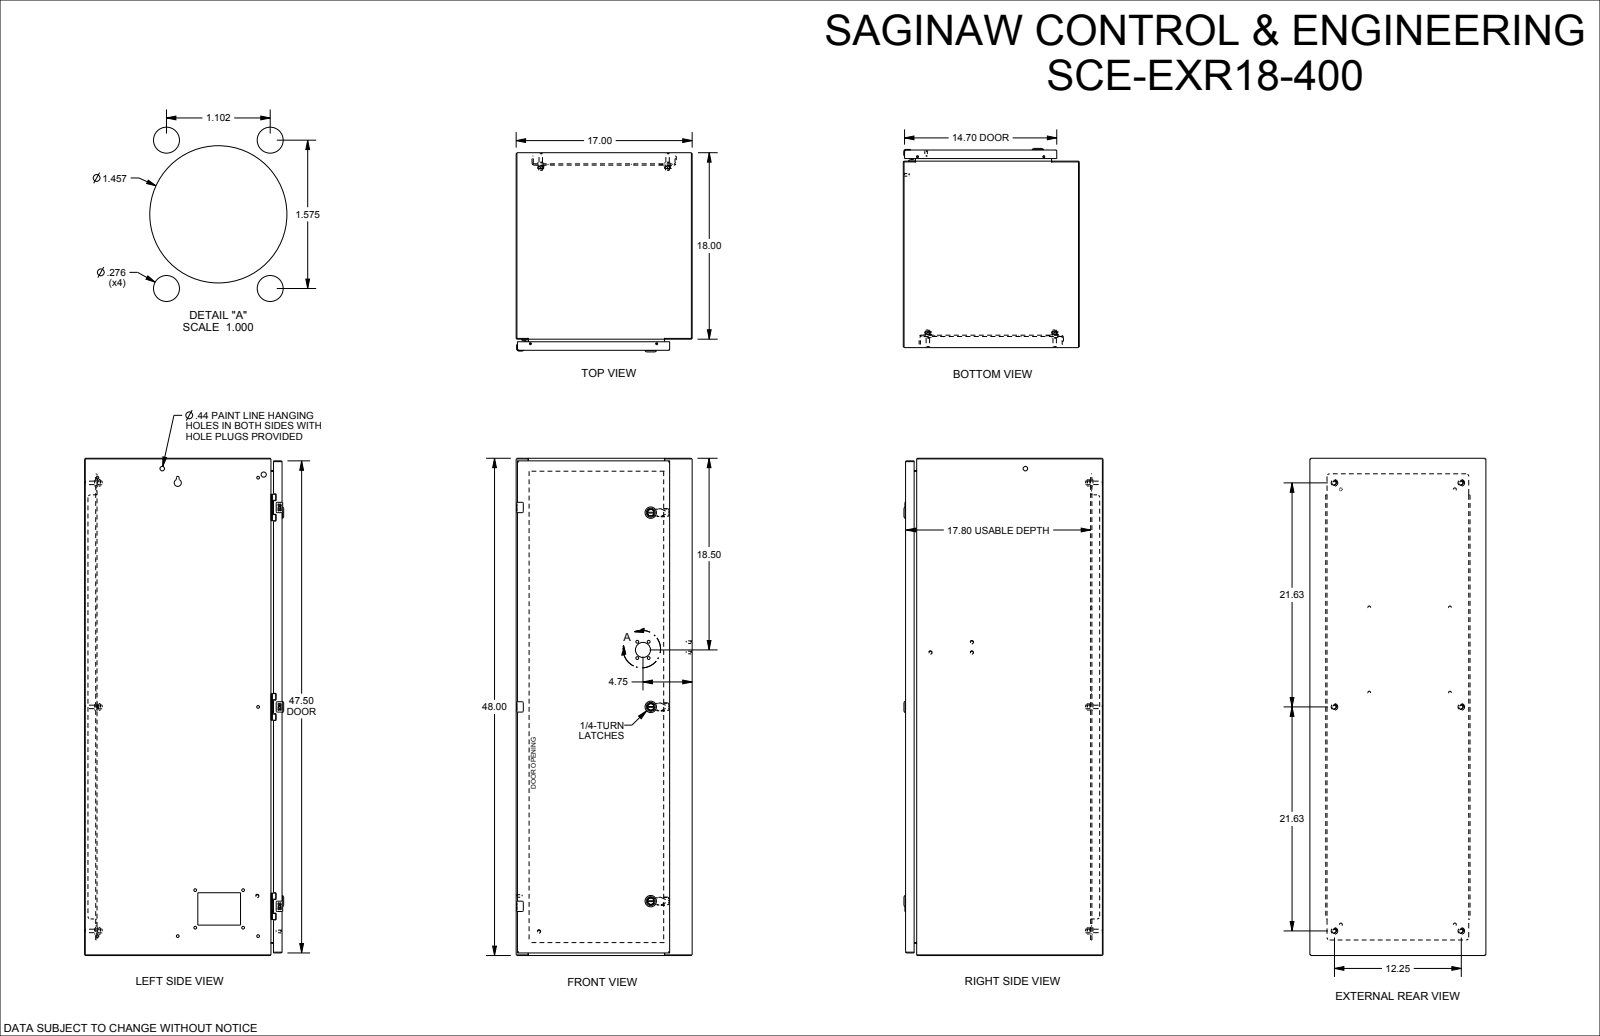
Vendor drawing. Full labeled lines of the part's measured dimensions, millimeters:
Part name (STEP PRODUCT): SCE-EXR18-400
STEP written by: SolidWorks 2019 (CONFIG_CONTROL_DESIGN)
Units: millimetres
Bodies: 0 solids, 3258 faces (1629 planar, 1016 cylindrical, 613 other)
Overall size (bounding box): 1219.2 × 488.4 × 431.8
Round holes (diameter × count): ⌀6.8 ×17, ⌀12.7 ×7, ⌀4.4 ×6, ⌀5.2 ×6, ⌀6.2 ×6, ⌀9.3 ×6, ⌀9.5 ×6, ⌀6.5 ×4, ⌀1 ×3, ⌀4 ×3, ⌀5 ×3, ⌀5.5 ×3
Round bosses / shafts (diameter × count): ⌀4.3 ×9, ⌀9.3 ×6, ⌀8.4 ×6, ⌀6.4 ×6, ⌀6.1 ×6, ⌀6.3 ×5, ⌀7 ×4, ⌀5 ×4
Partial cylindrical surfaces — rounded edges, fillets, slot ends (radius × count): R0.3 ×82, R0.4 ×44, R0.3 ×36, R0.5 ×28, R0.6 ×18, R2.5 ×16, R0.8 ×15, R0.8 ×14
Main face-to-face distances: 1.9, 1.9, 429.9, 482.5, 428, 431.8, 480.6, 484.5, 28.6, 25.4
Hole centre spacings: 489, 25, 977.9, 0.5, 12.5, 12.5, 463.9, 476.4
